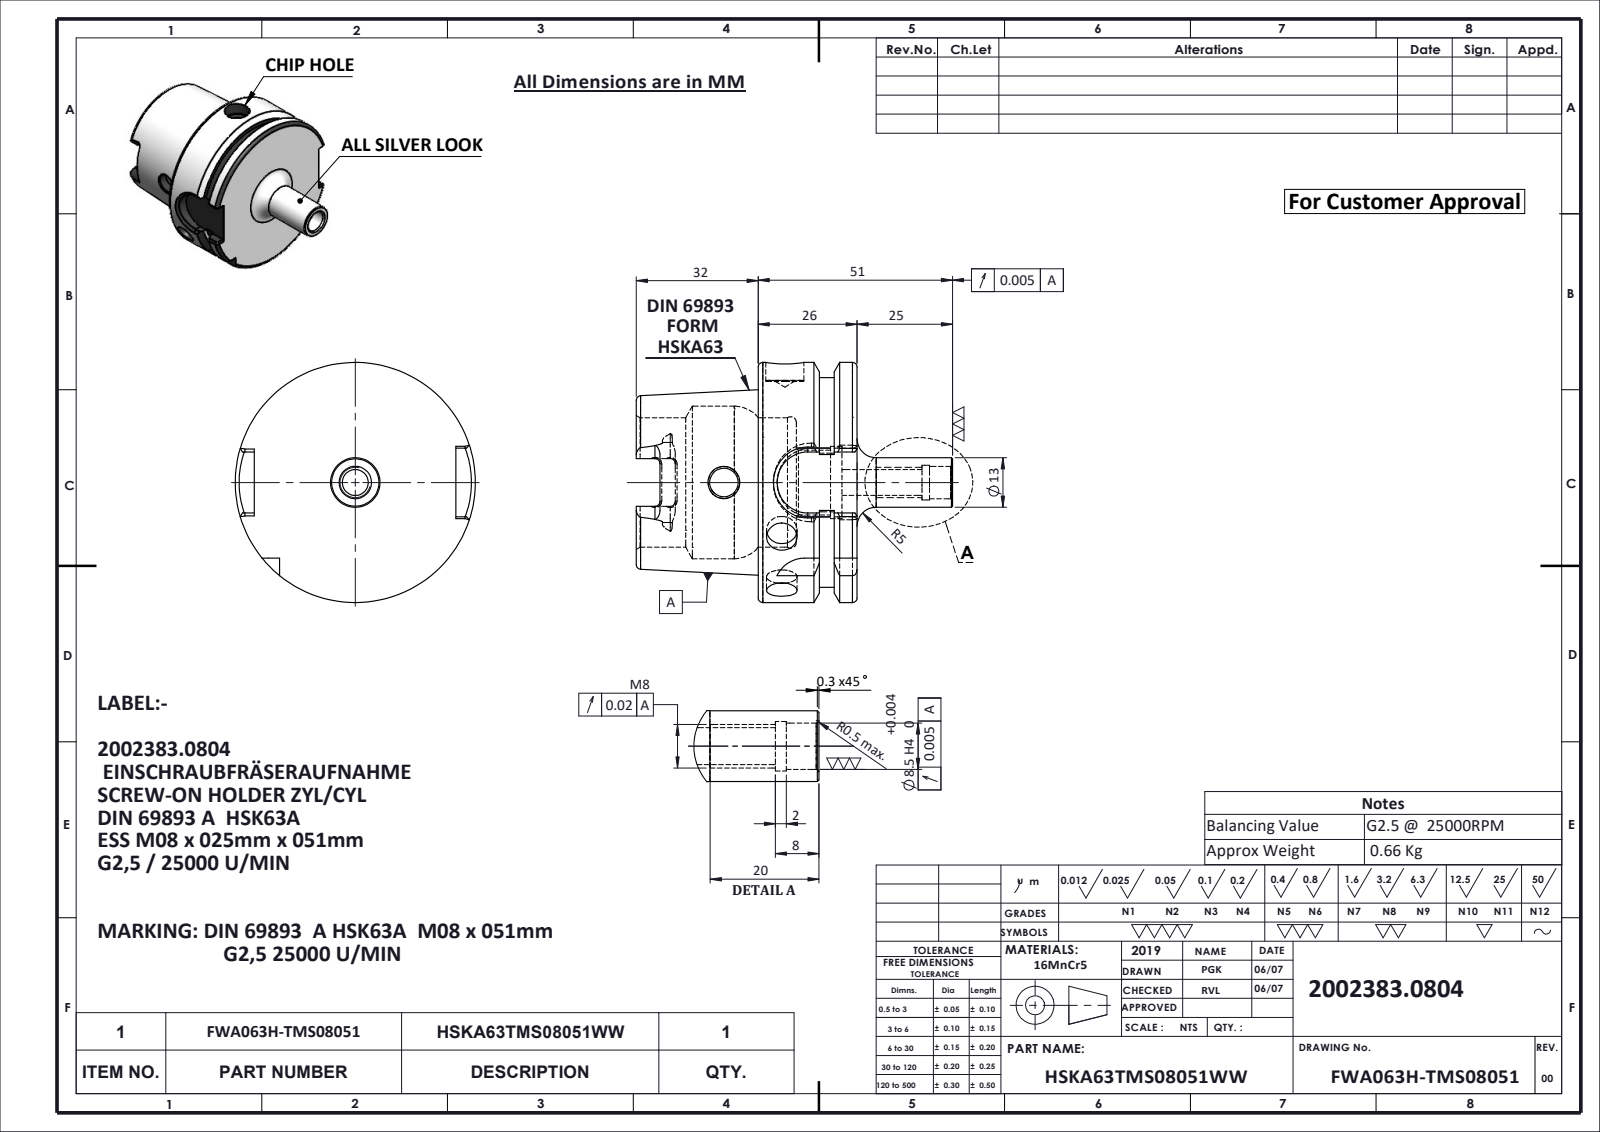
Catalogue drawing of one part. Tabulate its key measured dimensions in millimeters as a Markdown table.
| quantity | value |
| --- | --- |
| part name | FWA063H-TMS08051; HSKA63TMS08051WW |
| STEP written by | SolidWorks 2024 (CONFIG_CONTROL_DESIGN) |
| units | millimeters |
| bodies | 1 solid, 164 faces (51 planar, 51 cylindrical, 62 other) |
| overall size | 83 × 63 × 63 |
| volume | 83 375 mm³ |
| surface area | 23 888 mm² |
| round holes (diameter × count) | 8 × 2, 6.8 × 1, 7.5 × 1, 8.5 × 1, 9.1 × 1, 10 × 1, 17 × 1, 19 × 1, 34 × 1, 40 × 1 |
| round bosses / shafts (diameter × count) | 63 × 1, 55 × 1, 13 × 1 |
| partial cylindrical surfaces (radius × count) | 1.3 × 6, 2.88 × 4, 8 × 2, 9 × 1 |
| main face-to-face distances | 25.95, 10, 15.95, 32, 42, 57.95, 52.9, 54, 22, 12 |
